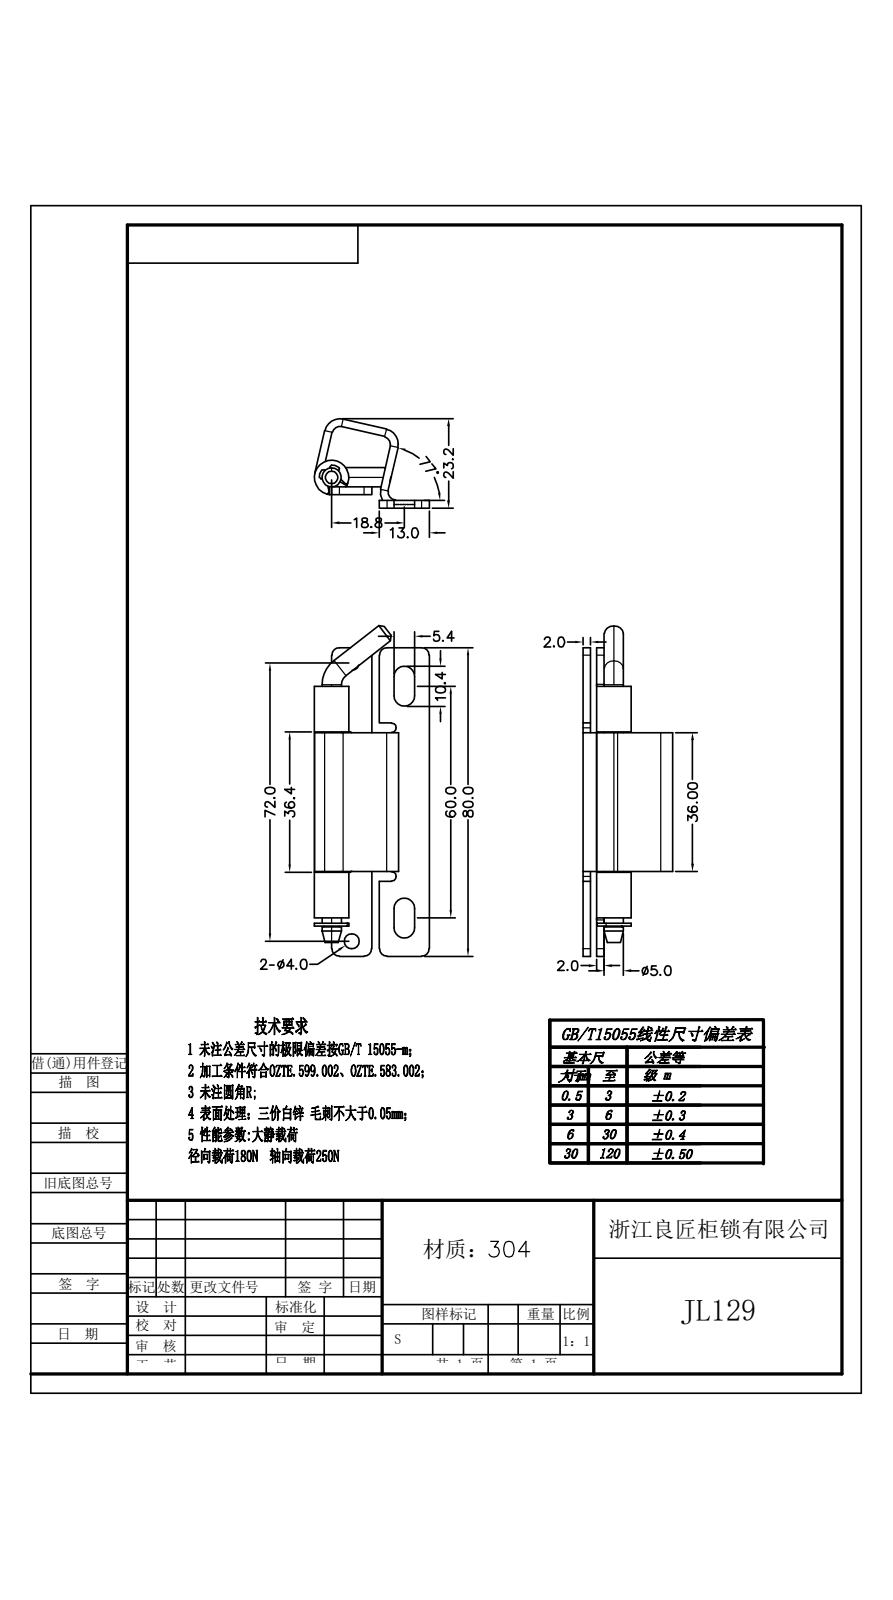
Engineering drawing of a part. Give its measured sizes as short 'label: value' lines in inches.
written by: Rhino 8.5 (CONFIG_CONTROL_DESIGN)
unit: in
bodies: 2 solids, 119 faces (52 planar, 57 cylindrical, 10 other)
size: 3.36 × 1.16 × 0.914
volume: 0.513 in³; area: 17.36 in²
holes: 2× ⌀0.157
bosses: 2× ⌀0.197, 1× ⌀0.354, 1× ⌀0.157
rounds: 13× R0.079, 4× R0.02, 4× R0.106, 3× R0.157, 2× R0.049
face distances: 0.079, 0.138, 0.689, 0.059, 0.217, 0.078, 0.767, 0.61, 0.618, 1.433
hole spacings: 2.843
